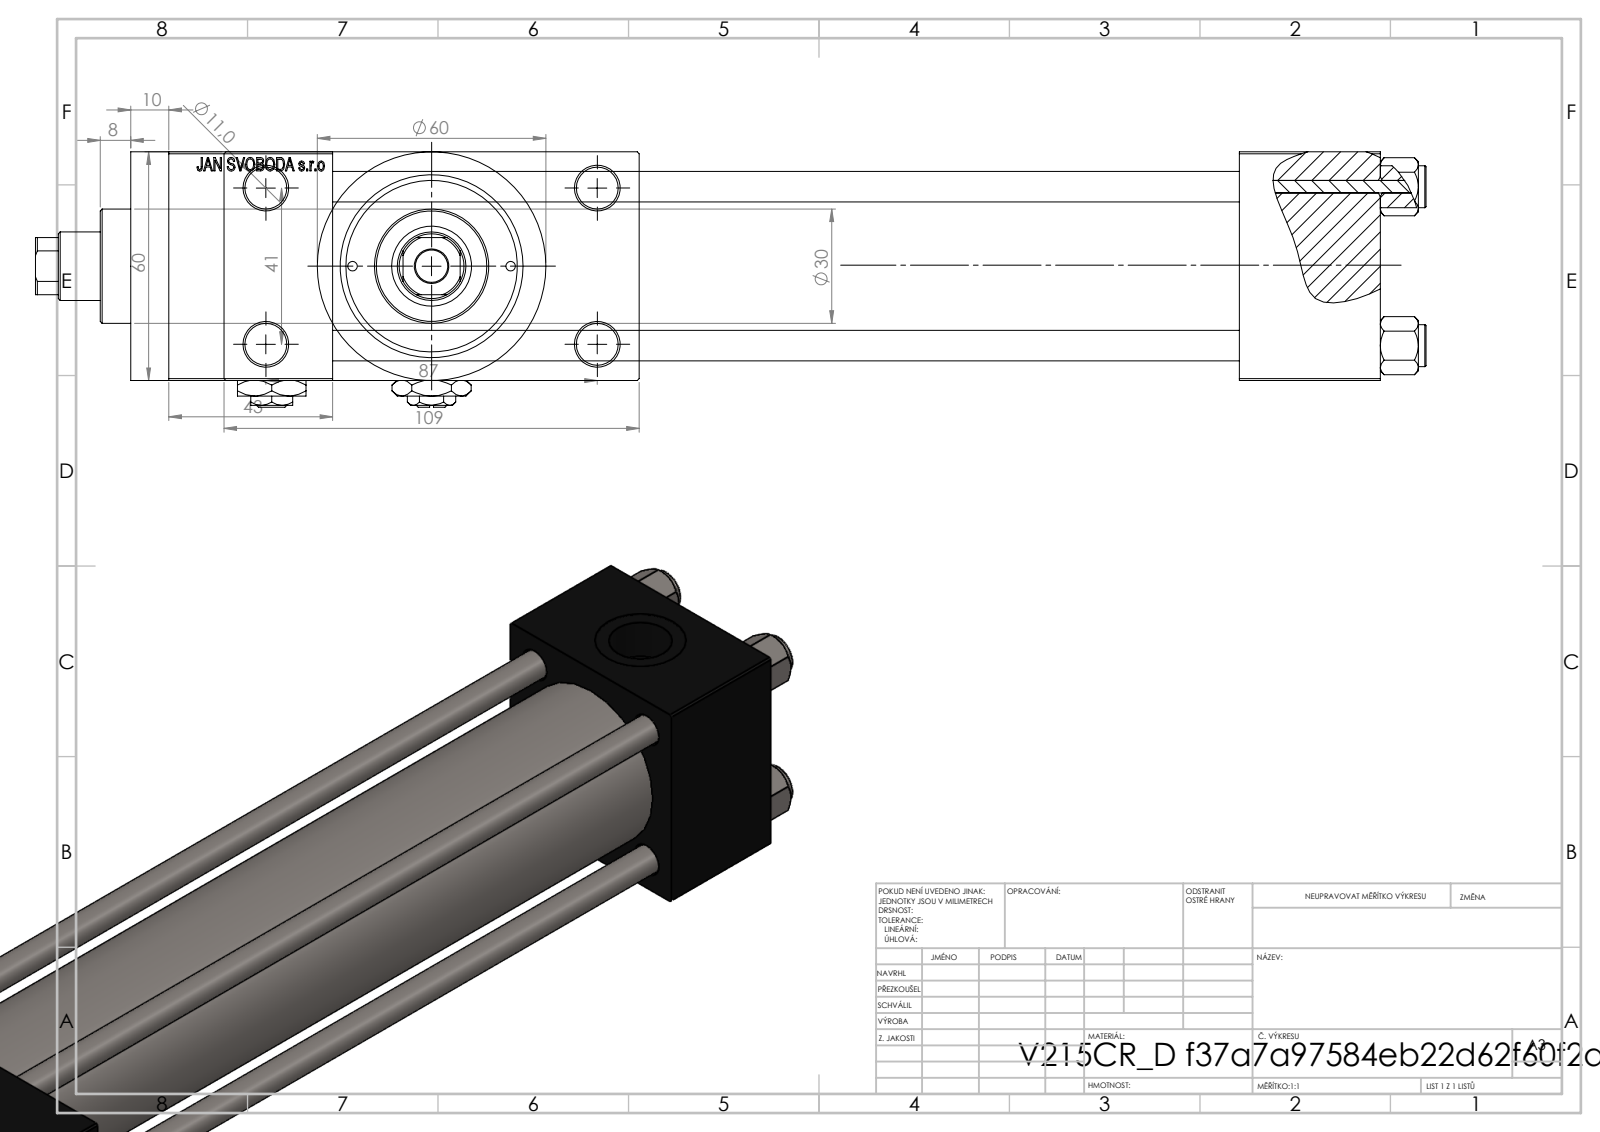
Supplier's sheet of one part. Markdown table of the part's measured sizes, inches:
| quantity | value |
| --- | --- |
| part name | V215_VC_A; V215CR_VCP_D; NUT_M5_D; V215CR_D_Body (+2 more) |
| STEP written by | SolidWorks 2019 (CONFIG_CONTROL_DESIGN) |
| units | inches |
| bodies | 12 solids, 1161 faces (524 planar, 97 cylindrical, 540 other) |
| overall size | 14.37 × 4.291 × 2.638 |
| volume | 41.01 in³ |
| surface area | 308.5 in² |
| round holes (diameter × count) | 0.315 × 4, 0.433 × 4, 0.098 × 2, 0.276 × 2, 0.656 × 2, 0.945 × 2, 0.335 × 1, 0.709 × 1, 0.827 × 1, 1.22 × 1, 1.575 × 1, 1.772 × 1 |
| round bosses / shafts (diameter × count) | 0.433 × 4, 2.362 × 1, 1.811 × 1, 1.181 × 1 |
| partial cylindrical surfaces (radius × count) | 0.335 × 1 |
| main face-to-face distances | 2.362, 0.965, 3.327, 9.37, 1.457, 10.827, 1.693, 12.52, 11.063, 4.291 |
| hole center spacings | 0.821, 0.892, 1.161, 1.206, 1.642, 1.832, 1.856, 1.893 |
